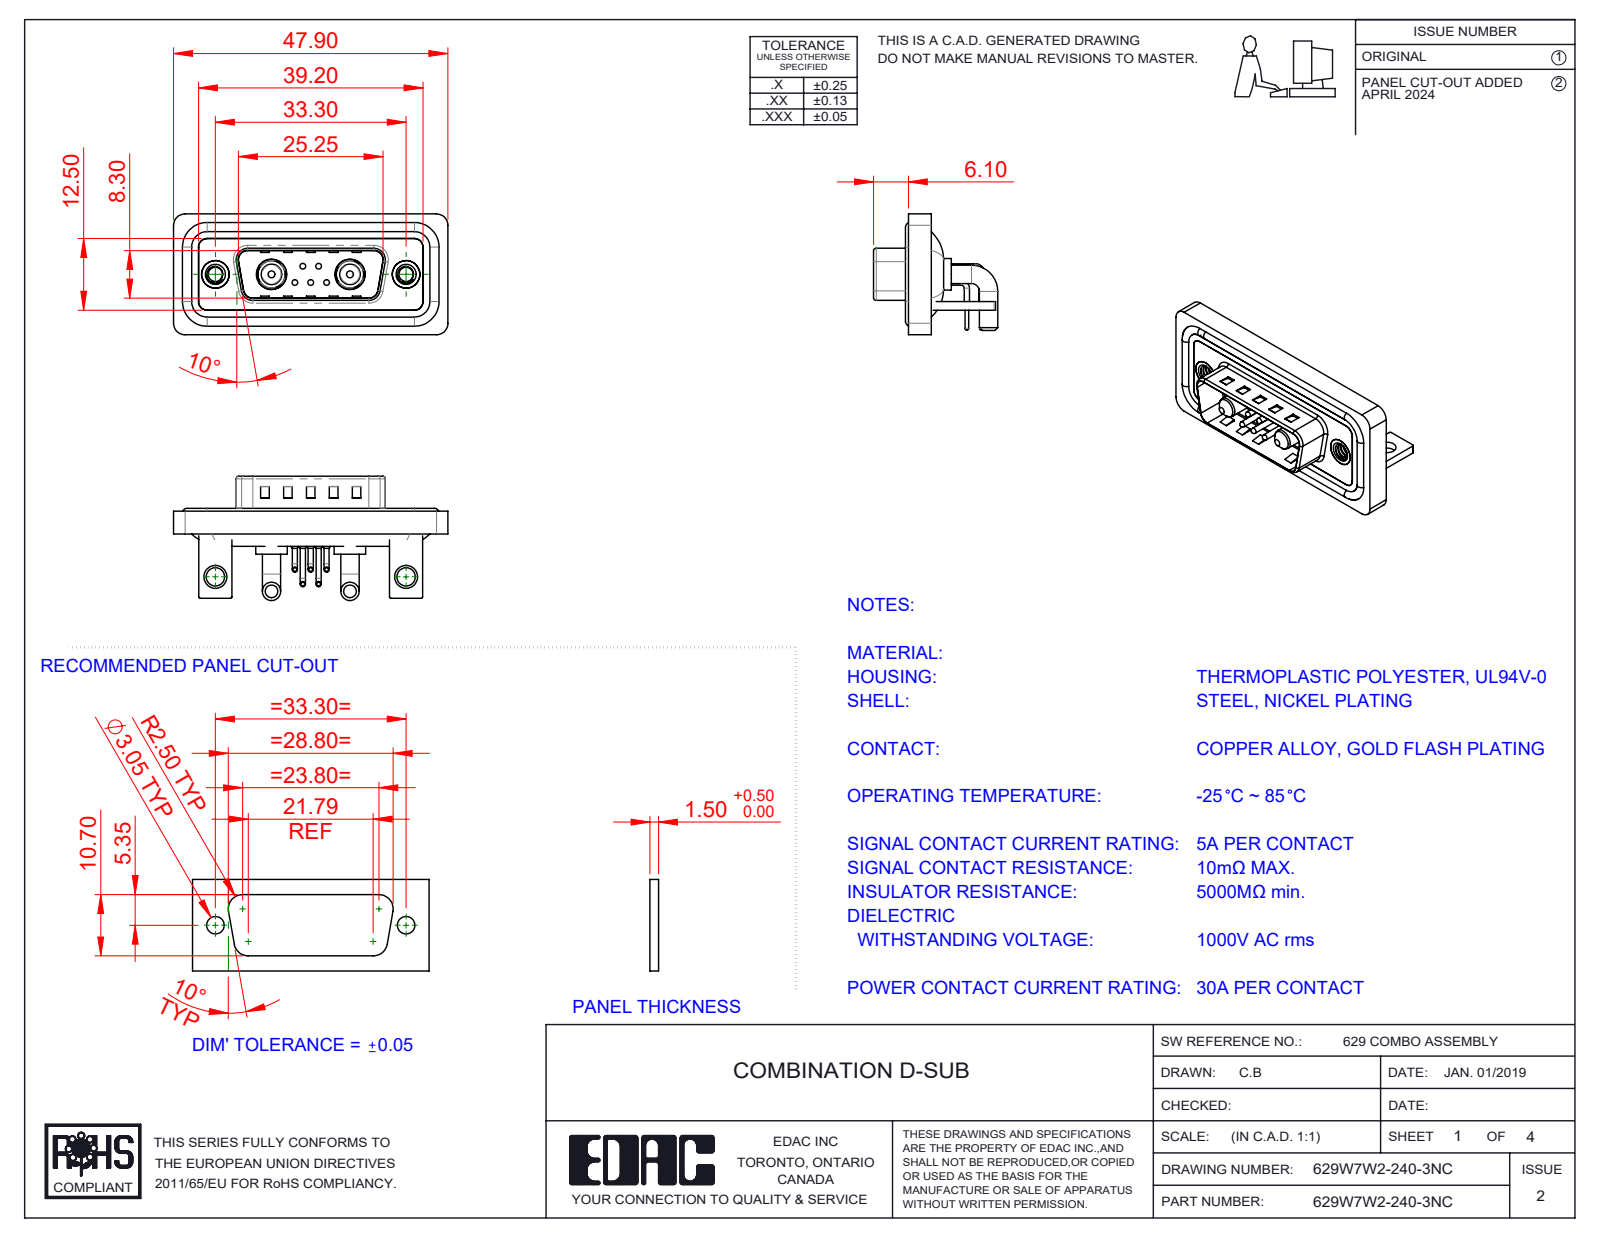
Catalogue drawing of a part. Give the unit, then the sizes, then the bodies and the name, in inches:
Units: inches
Overall size (bounding box): 1.886 × 0.854 × 0.831
Round holes (diameter × count): ⌀0.03 ×5, ⌀0.063 ×5, ⌀0.079 ×5, ⌀0.098 ×2, ⌀0.126 ×2, ⌀0.157 ×2, ⌀0.189 ×2, ⌀0.191 ×2, ⌀0.197 ×2, ⌀0.209 ×2
Round bosses / shafts (diameter × count): ⌀0.035 ×10, ⌀0.059 ×5, ⌀0.039 ×5, ⌀0.026 ×5, ⌀0.126 ×4, ⌀0.063 ×4, ⌀0.217 ×2, ⌀0.205 ×2
Partial cylindrical surfaces — rounded edges, fillets, slot ends (radius × count): R0.079 ×21, R0.059 ×18, R0.01 ×16, R0.02 ×9, R0.063 ×8, R0.04 ×5, R0.024 ×4, R0.026 ×4
Main face-to-face distances: 0.016, 0.059, 0.031, 0.114, 0.083, 0.043, 0.063, 0.047, 0.146, 0.177
Hole centre spacings: 0.124, 0.109, 0.386, 0.925, 1.311, 0.17, 0.17, 0.198
Volume: 0.367 in³ · Surface area: 15.14 in²
Bodies: 18 solids, 1121 faces (537 planar, 424 cylindrical, 160 other)
Part name (STEP PRODUCT): Power Pin_30A RA; 629Combo Threaded Rivet_B; 629Combo Contact Row 1; 629Combo Stabilizer Bracket (+6 more)
STEP written by: SolidWorks 2023 (CONFIG_CONTROL_DESIGN)
